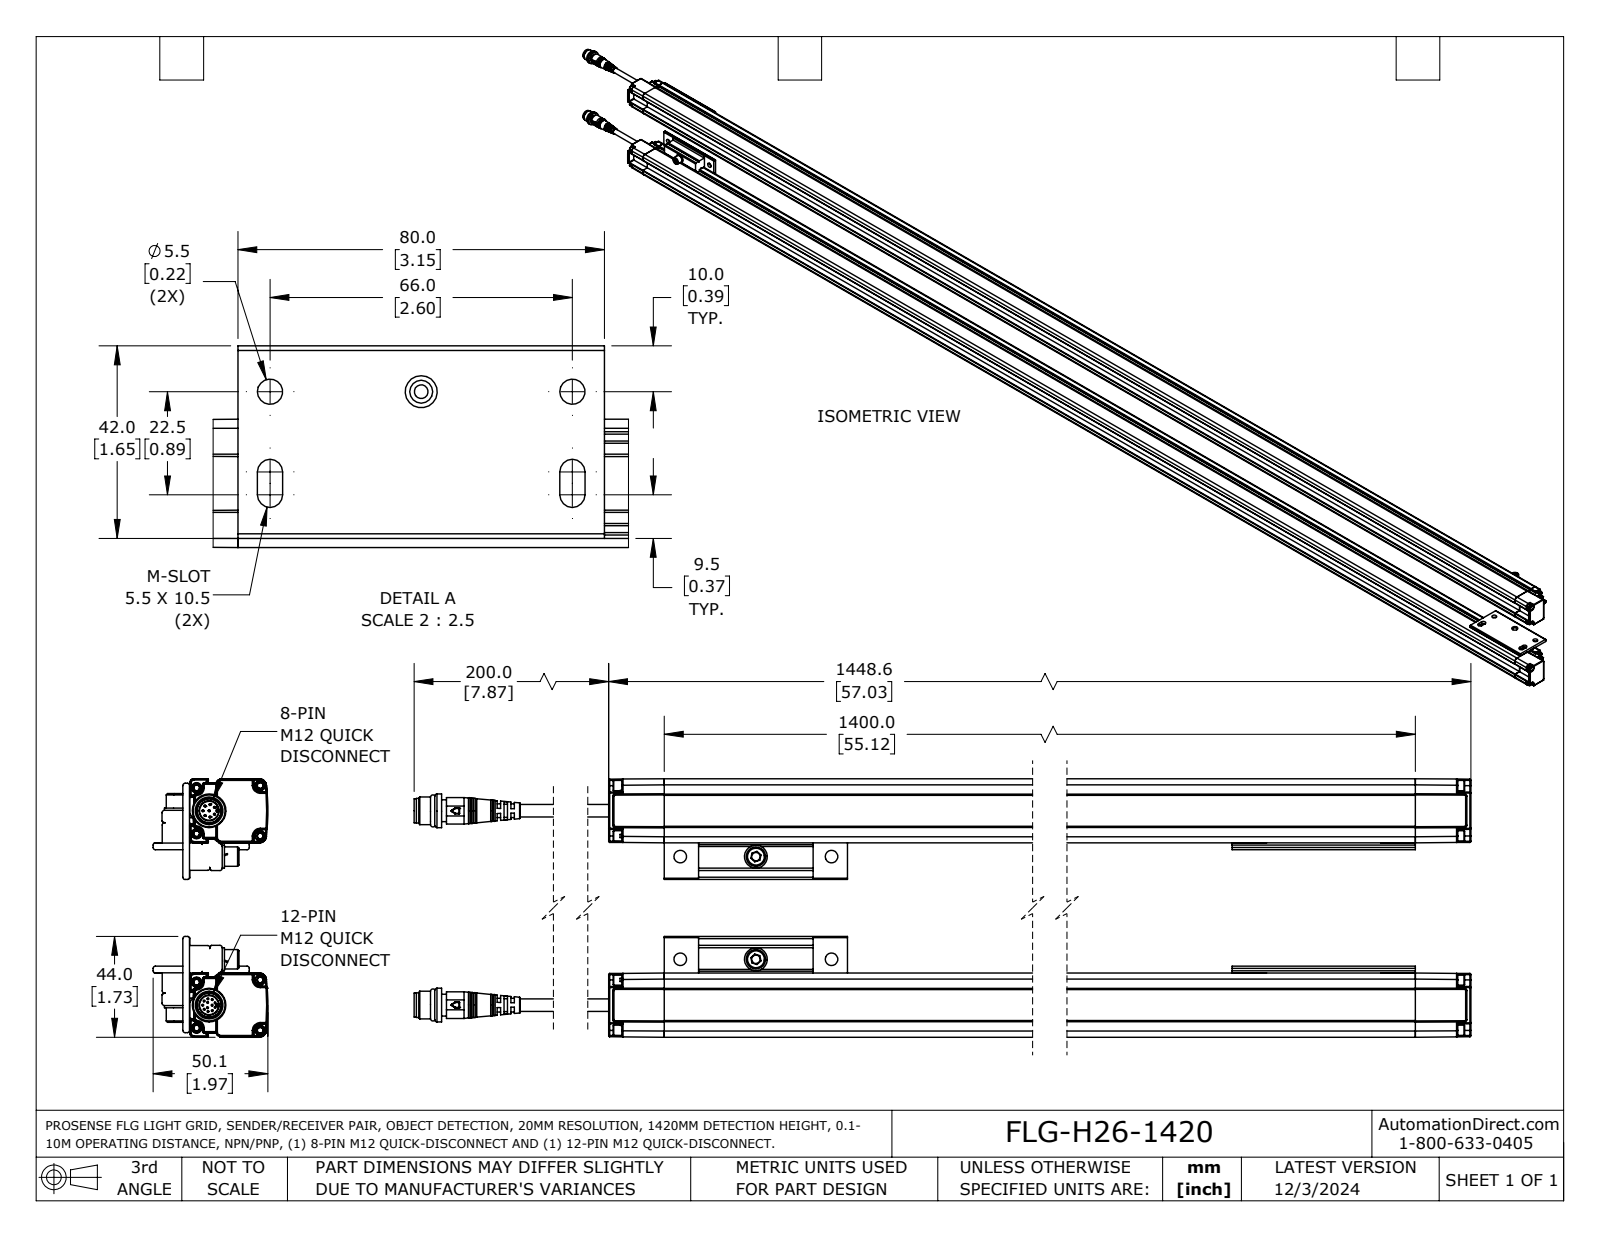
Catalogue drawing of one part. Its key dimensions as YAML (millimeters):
part_name: "FLG-H26-1420"
step_written_by: "SolidWorks 2023 (AUTOMOTIVE_DESIGN)"
units: millimeters
bodies: {solids: 10, faces: 1668, planar: 816, cylindrical: 456, other: 396}
overall_size: [1540.55, 112.8, 50.09]
volume: 2319000
surface_area: 564505
round_holes:
  - {diameter: 0.4, count: 16}
  - {diameter: 5.5, count: 6}
  - {diameter: 2.5, count: 4}
  - {diameter: 5, count: 3}
  - {diameter: 8.3, count: 2}
round_bosses_or_shafts:
  - {diameter: 0.8, count: 20}
  - {diameter: 4.5, count: 8}
  - {diameter: 3, count: 8}
  - {diameter: 5.5, count: 4}
  - {diameter: 1.5, count: 4}
  - {diameter: 10, count: 3}
  - {diameter: 8.5, count: 3}
  - {diameter: 3.7, count: 3}
partial_cylinders:
  - {radius: 0.5, count: 142}
  - {radius: 1, count: 40}
  - {radius: 0.25, count: 20}
  - {radius: 0.2, count: 12}
  - {radius: 0.3, count: 12}
  - {radius: 2.75, count: 12}
  - {radius: 2.55, count: 6}
  - {radius: 1.25, count: 4}
face_to_face_distances: [84.8, 28, 1.8, 7.25, 20.75, 24.65, 56.8, 112.8, 26.45, 5.45]
hole_center_spacings: [2.75, 33, 4.15, 24.87, 55.64, 5.45, 44.8, 66]
